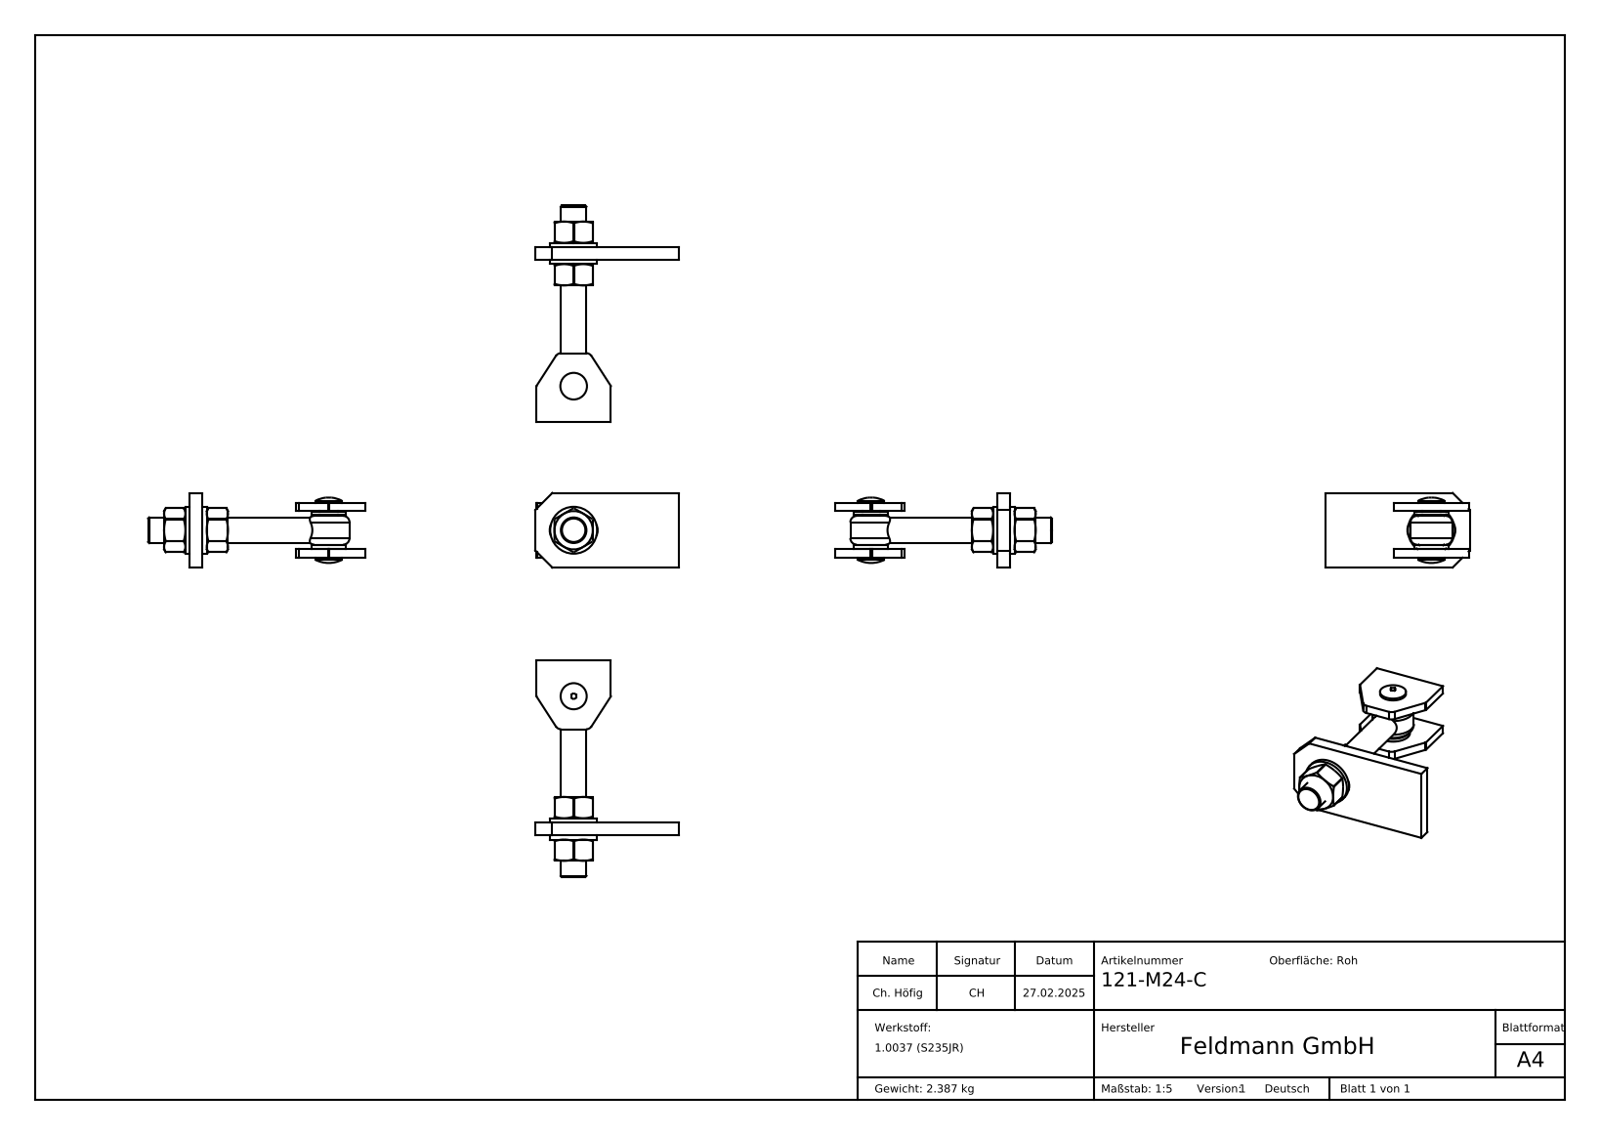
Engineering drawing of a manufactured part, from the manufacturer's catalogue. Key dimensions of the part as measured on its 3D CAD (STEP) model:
Part name (STEP PRODUCT): 121-MXX-C Teil2_121-M24-C Teil2; 121-MXX-C Teil1_121-M24-C Teil1; 121-MXX-C Teil6_121-M24-C Teil6; 121-M24-C (+5 more)
STEP written by: SolidWorks 2018 (CONFIG_CONTROL_DESIGN)
Units: millimetres
Bodies: 12 solids, 408 faces (219 planar, 62 cylindrical, 127 other)
Overall size (bounding box): 203.5 × 135 × 70
Volume: 305 700 mm³ · Surface area: 84 860 mm²
Round holes (diameter × count): ⌀8.5 ×1, ⌀17.2 ×1, ⌀17.5 ×1, ⌀21 ×1, ⌀25 ×1
Round bosses / shafts (diameter × count): ⌀44 ×1, ⌀39 ×1, ⌀32 ×1, ⌀25 ×1, ⌀24.5 ×1, ⌀24 ×1, ⌀16.8 ×1, ⌀10 ×1
Partial cylindrical surfaces — rounded edges, fillets, slot ends (radius × count): R0.5 ×6, R3 ×2, R6 ×2, R13.25 ×2, R8.7 ×1
Main face-to-face distances: 12, 8, 43.5, 51.5, 35.5, 36, 4, 16, 20, 9.25
